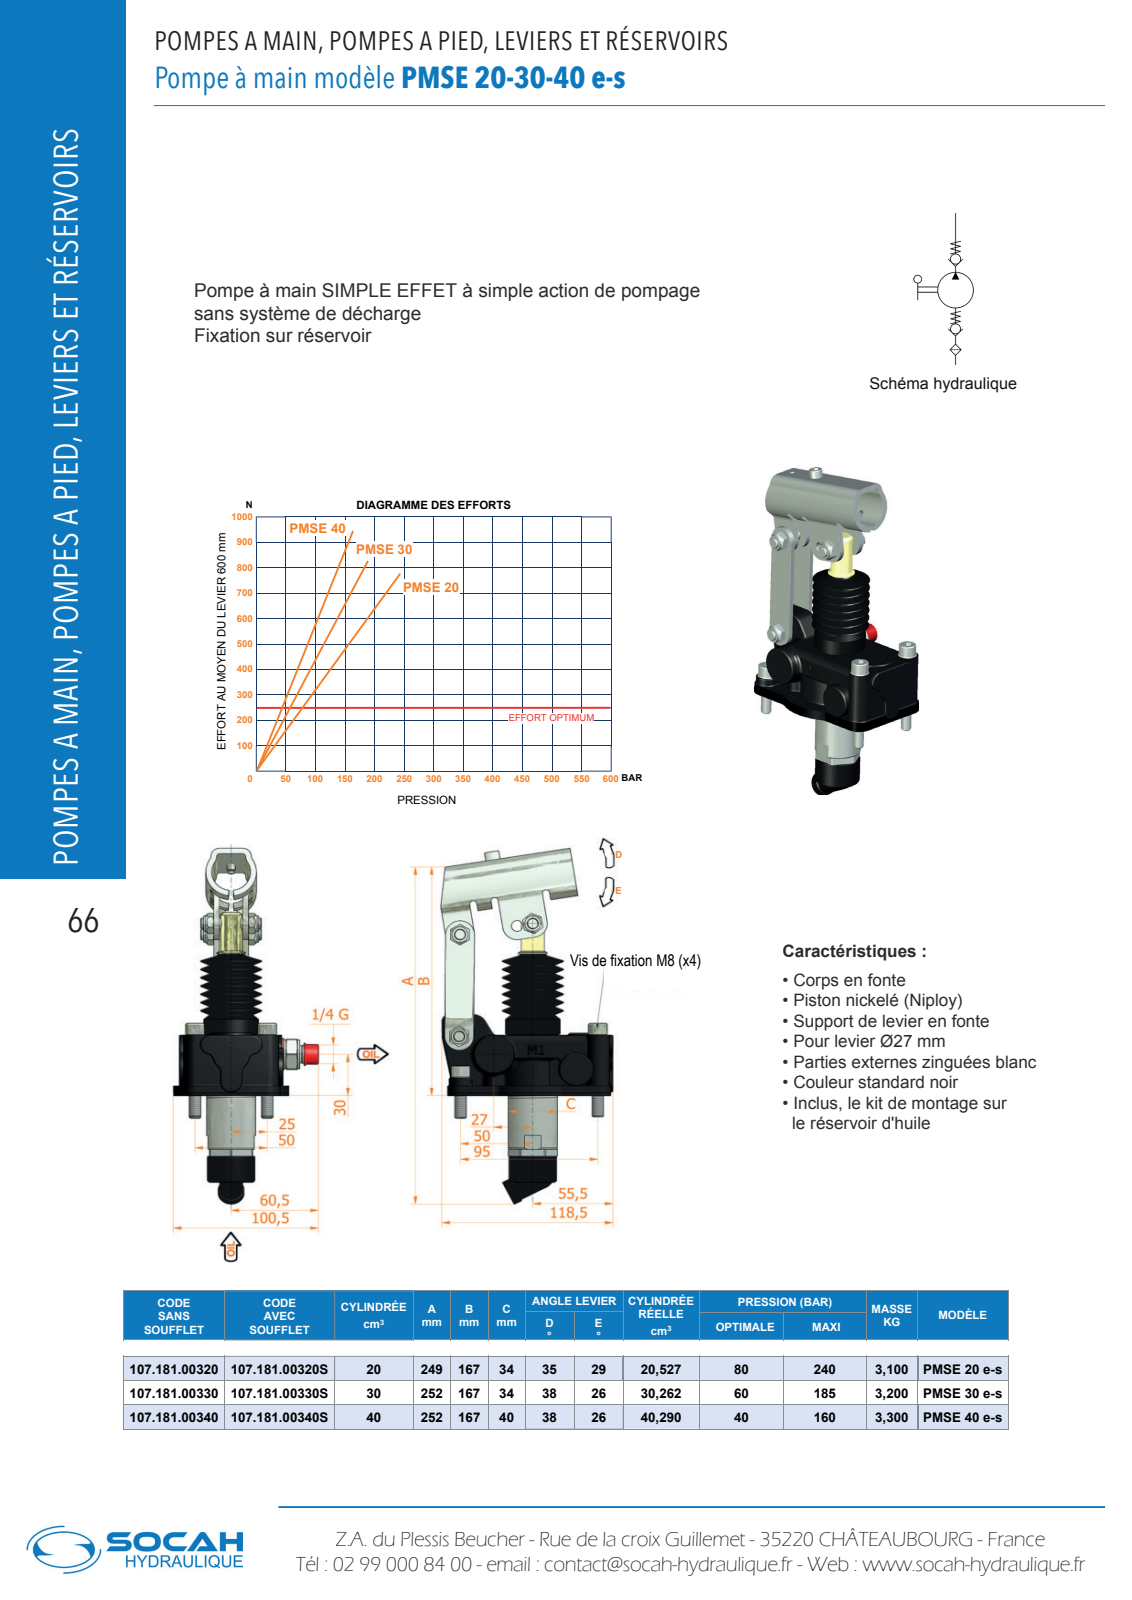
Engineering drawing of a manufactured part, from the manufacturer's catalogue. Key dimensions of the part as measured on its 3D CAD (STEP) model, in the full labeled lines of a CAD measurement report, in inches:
Part name (STEP PRODUCT): 6067.0039.00
STEP written by: Autodesk Inventor 2013 (CONFIG_CONTROL_DESIGN)
Units: inches
Bodies: 12 solids, 1404 faces (658 planar, 315 cylindrical, 431 other)
Overall size (bounding box): 10.18 × 4.693 × 3.957
Volume: 18.22 in³ · Surface area: 208.9 in²
Round holes (diameter × count): ⌀0.315 ×6, ⌀0.551 ×4, ⌀0.157 ×1, ⌀0.197 ×1, ⌀0.709 ×1, ⌀0.866 ×1, ⌀1.142 ×1
Round bosses / shafts (diameter × count): ⌀0.512 ×4, ⌀0.472 ×4, ⌀0.335 ×4, ⌀0.435 ×3, ⌀0.315 ×3, ⌀0.787 ×2, ⌀1.496 ×1, ⌀1.339 ×1
Partial cylindrical surfaces — rounded edges, fillets, slot ends (radius × count): R0.039 ×30, R0.008 ×24, R0.004 ×16, R0.197 ×16, R0.079 ×14, R0.118 ×9, R0.315 ×9, R0.014 ×6
Main face-to-face distances: 0.157, 0.079, 1.654, 0.787, 0.63, 1.732, 0.197, 1.457, 0.276, 0.945
Hole centre spacings: 1.969, 2.027, 2.201, 3.74, 4.226, 3.727
